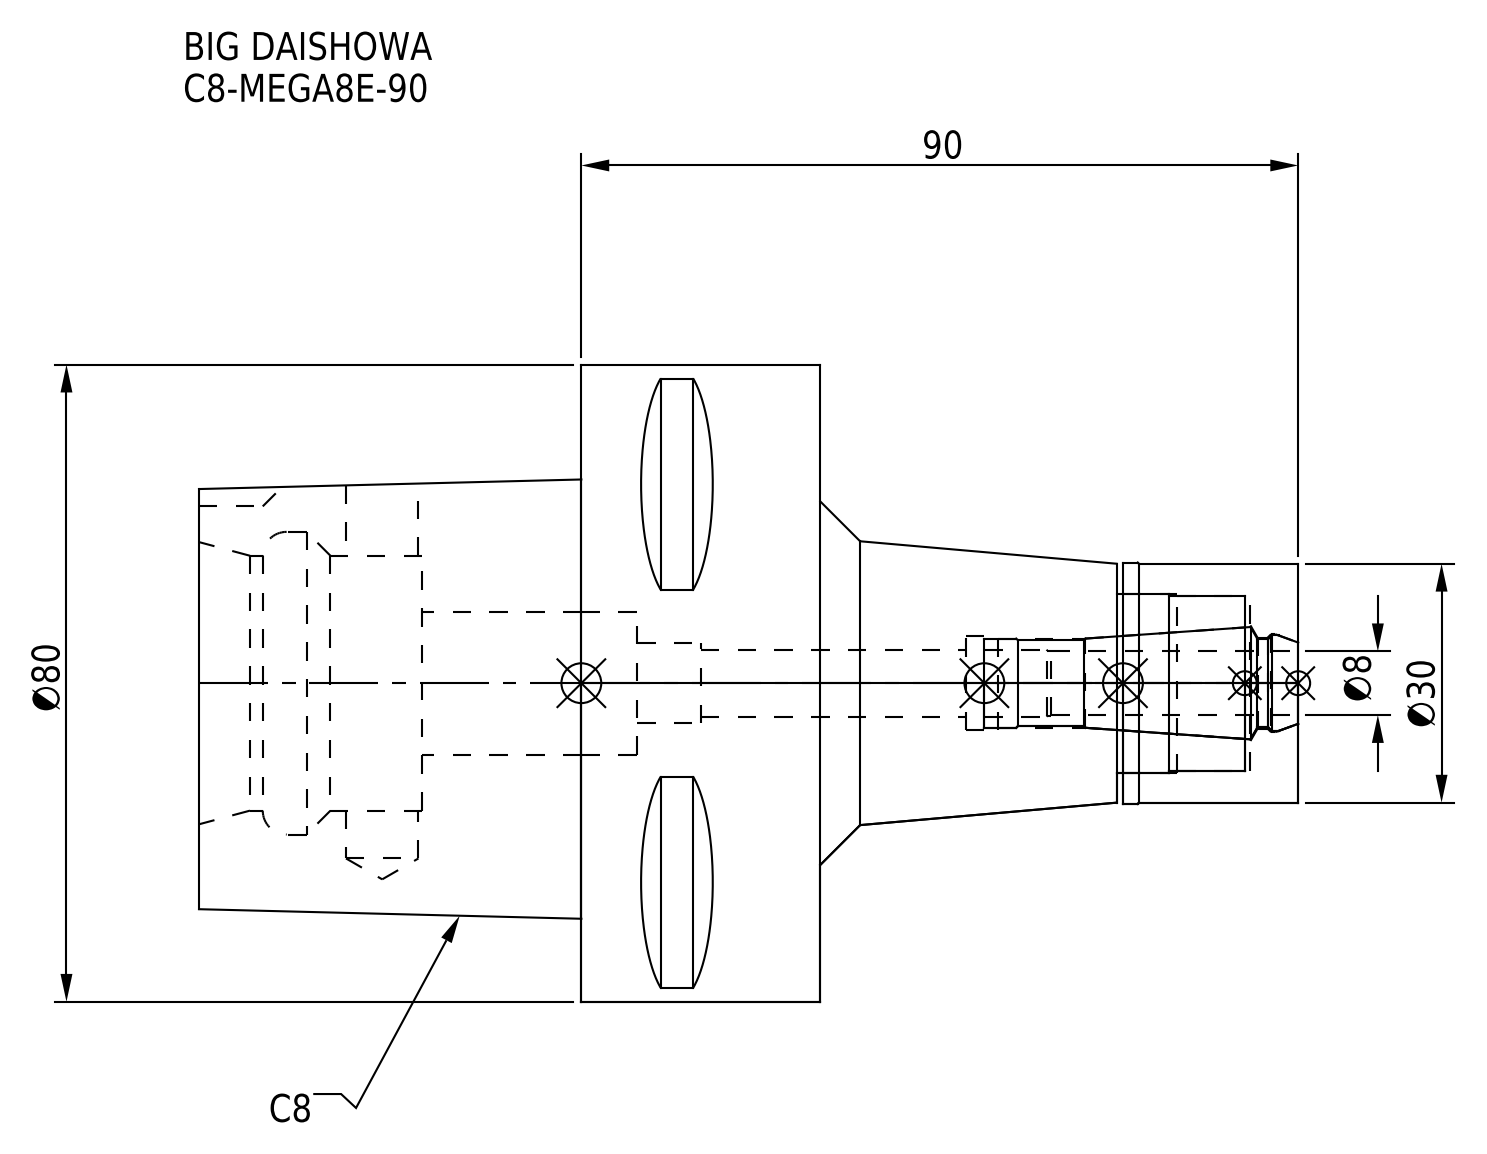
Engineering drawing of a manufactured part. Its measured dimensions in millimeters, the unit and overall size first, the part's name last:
Units: millimetres
Overall size (bounding box): 138 × 80 × 80
Round holes (diameter × count): ⌀8.4 ×1, ⌀9.1 ×1, ⌀10 ×1, ⌀11.2 ×1, ⌀11.4 ×1, ⌀11.8 ×1, ⌀12.3 ×1, ⌀18 ×1, ⌀22 ×1, ⌀22.5 ×1, ⌀32 ×1, ⌀38 ×1
Round bosses / shafts (diameter × count): ⌀80 ×1, ⌀30.3 ×1, ⌀30 ×1
Partial cylindrical surfaces — rounded edges, fillets, slot ends (radius × count): R6 ×1
Main face-to-face distances: 30, 78, 48, 60, 90, 138, 20, 110, 50, 28
Volume: 265 454 mm³ · Surface area: 42 425 mm²
Bodies: 2 solids, 100 faces (37 planar, 39 cylindrical, 24 other)
Part name (STEP PRODUCT): C8-MEGA8E-90-080.stp; C8-MEGA8E-90_1.stp; C8-MEGA8E-90; MEN8_1.stp (+3 more)
STEP written by: SolidWorks 2019 (CONFIG_CONTROL_DESIGN)
